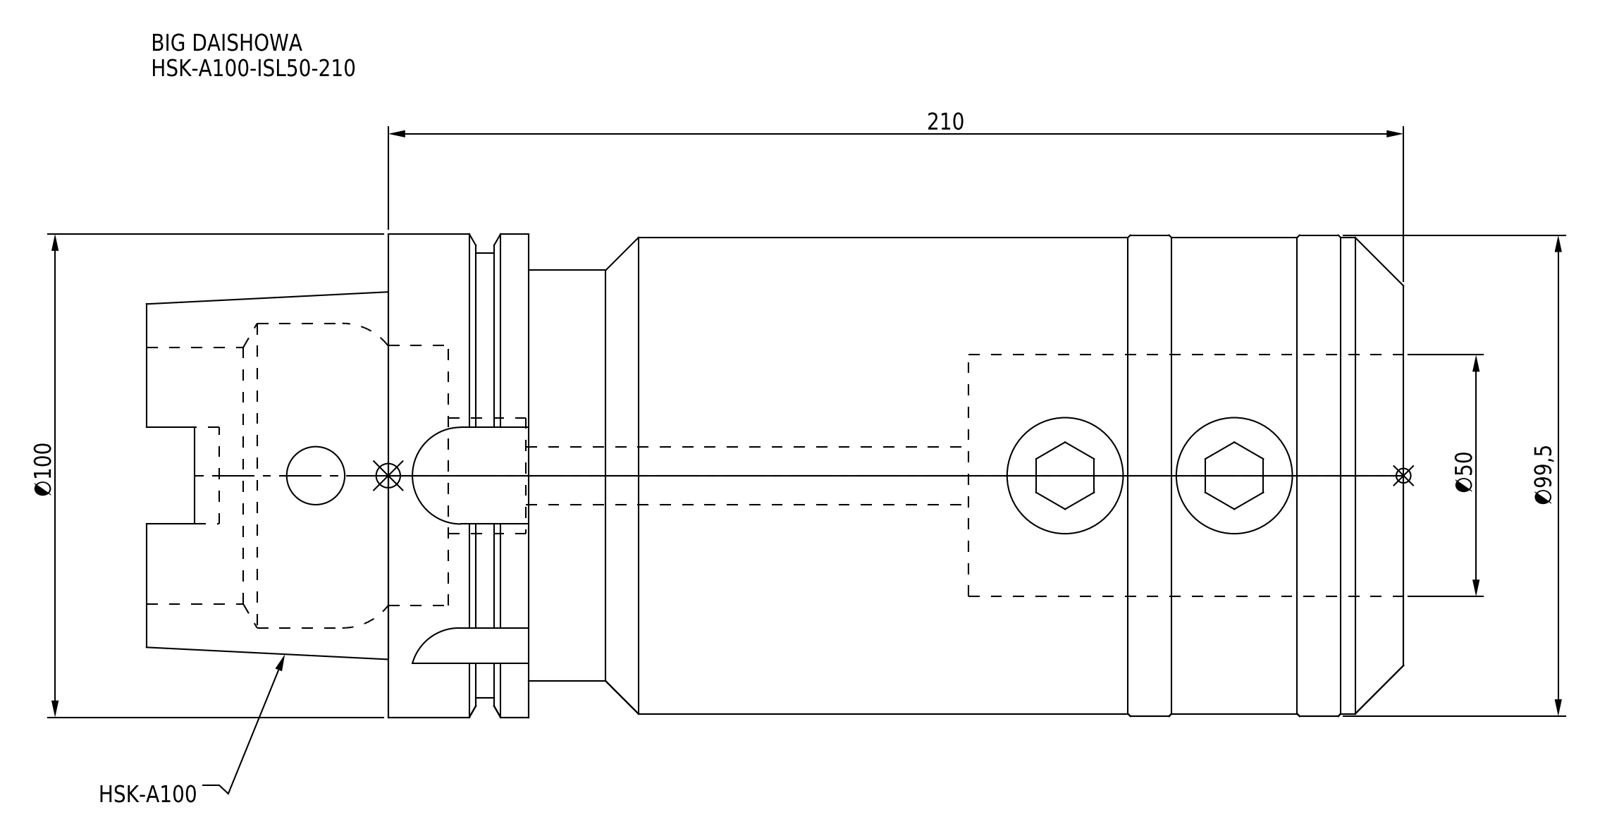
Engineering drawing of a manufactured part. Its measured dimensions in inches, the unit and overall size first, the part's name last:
Units: inches
Overall size (bounding box): 10.236 × 3.937 × 3.937
Round holes (diameter × count): ⌀0.472 ×2, ⌀0.945 ×1, ⌀1.969 ×1, ⌀2.087 ×1, ⌀2.118 ×1, ⌀2.48 ×1
Round bosses / shafts (diameter × count): ⌀3.937 ×1, ⌀3.917 ×1, ⌀3.878 ×1, ⌀3.622 ×1, ⌀3.346 ×1
Partial cylindrical surfaces — rounded edges, fillets, slot ends (radius × count): R0.394 ×4
Main face-to-face distances: 8.268, 7.126, 1.142, 3.543, 3.583, 4.724, 7.778, 4.234, 0.652, 0.49
Volume: 85.25 in³ · Surface area: 192.2 in²
Bodies: 1 solid, 95 faces (29 planar, 42 cylindrical, 24 other)
Part name (STEP PRODUCT): HSK-A100-ISL50-210
STEP written by: CREO PARAMETRIC BY PTC INC, 2016380 (AUTOMOTIVE_DESIGN)
